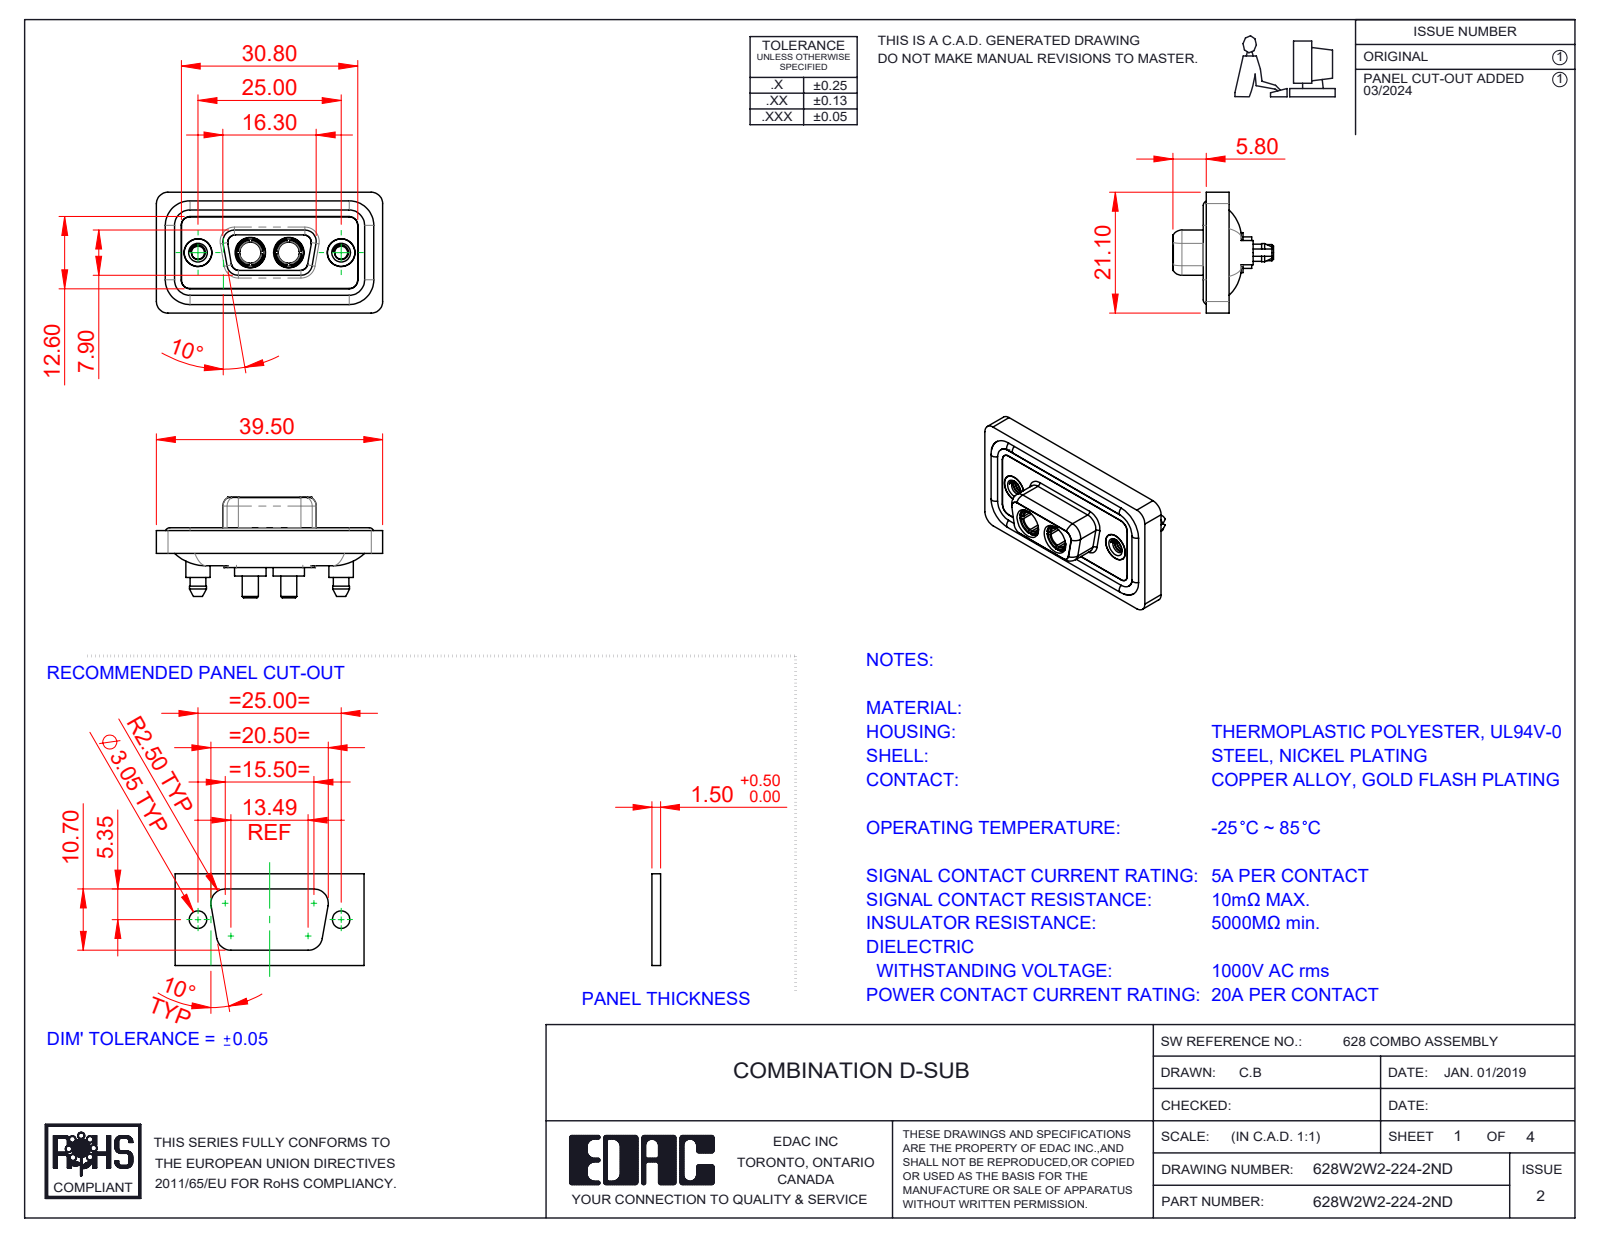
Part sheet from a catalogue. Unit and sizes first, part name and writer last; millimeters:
Units: millimetres
Overall size (bounding box): 39.5 × 21.1 × 17.55
Round holes (diameter × count): ⌀4.85 ×4, ⌀2.26 ×2, ⌀3.7 ×2, ⌀4 ×2, ⌀4.05 ×2, ⌀5 ×2, ⌀5.3 ×2
Round bosses / shafts (diameter × count): ⌀1.6 ×4, ⌀5.5 ×2, ⌀5.4 ×2, ⌀5.2 ×2, ⌀4.96 ×2, ⌀4.95 ×2, ⌀4.8 ×2, ⌀4.75 ×2
Partial cylindrical surfaces — rounded edges, fillets, slot ends (radius × count): R1.5 ×24, R2 ×18, R1.6 ×10, R1.35 ×8, R0.25 ×4, R0.5 ×4, R0.6 ×4, R0.65 ×4
Main face-to-face distances: 0.4, 1.8, 1.1, 2.9, 1.6, 0.5, 5.65, 7.45, 1.5, 4
Hole centre spacings: 9.14, 15.86, 6.72, 25
Volume: 4 848 mm³ · Surface area: 7 975 mm²
Bodies: 11 solids, 600 faces (179 planar, 282 cylindrical, 139 other)
Part name (STEP PRODUCT): 628Combo Housing_2W2; 628Combo Shell Front_09 Contacts; Power Socket_20A S; 628W2W2-224-2ND (+3 more)
STEP written by: SolidWorks 2023 (CONFIG_CONTROL_DESIGN)
